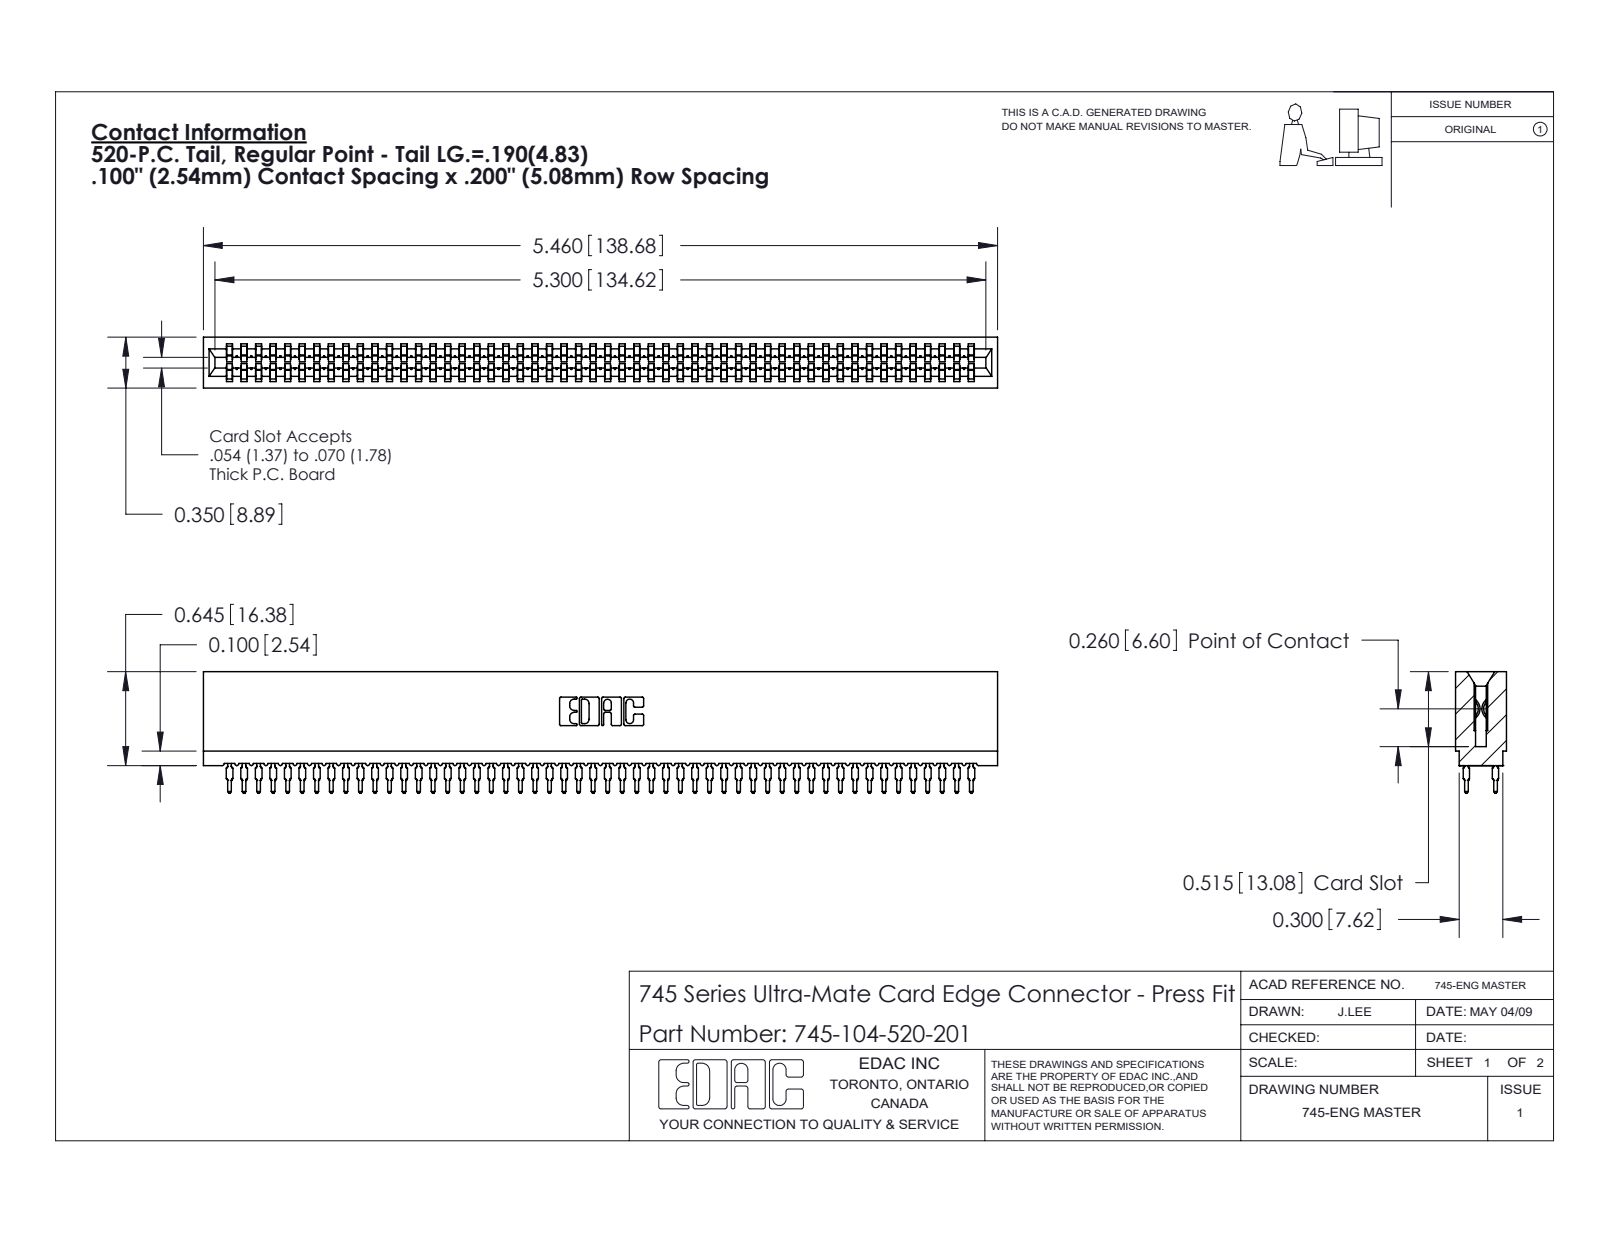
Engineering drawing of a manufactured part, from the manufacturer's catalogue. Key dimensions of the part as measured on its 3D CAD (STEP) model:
Part name (STEP PRODUCT): 745-292-001_520; 745-104-520-201; 745 Part_Insulator Option - 01
STEP written by: SolidWorks 2020 (CONFIG_CONTROL_DESIGN)
Units: inches
Bodies: 105 solids, 9403 faces (4839 planar, 1860 cylindrical, 2704 other)
Overall size (bounding box): 5.46 × 0.836 × 0.35
Volume: 0.753 in³ · Surface area: 38.51 in²
Partial cylindrical surfaces — rounded edges, fillets, slot ends (radius × count): R0.021 ×208, R0.015 ×104, R0.01 ×22, R0.005 ×8, R0.011 ×8, R0.007 ×6, R0.031 ×6, R0.026 ×3
Main face-to-face distances: 0.35, 0.063, 0.287, 0.045, 0.305, 0.018, 0.243, 0.138, 0.212, 0.093
